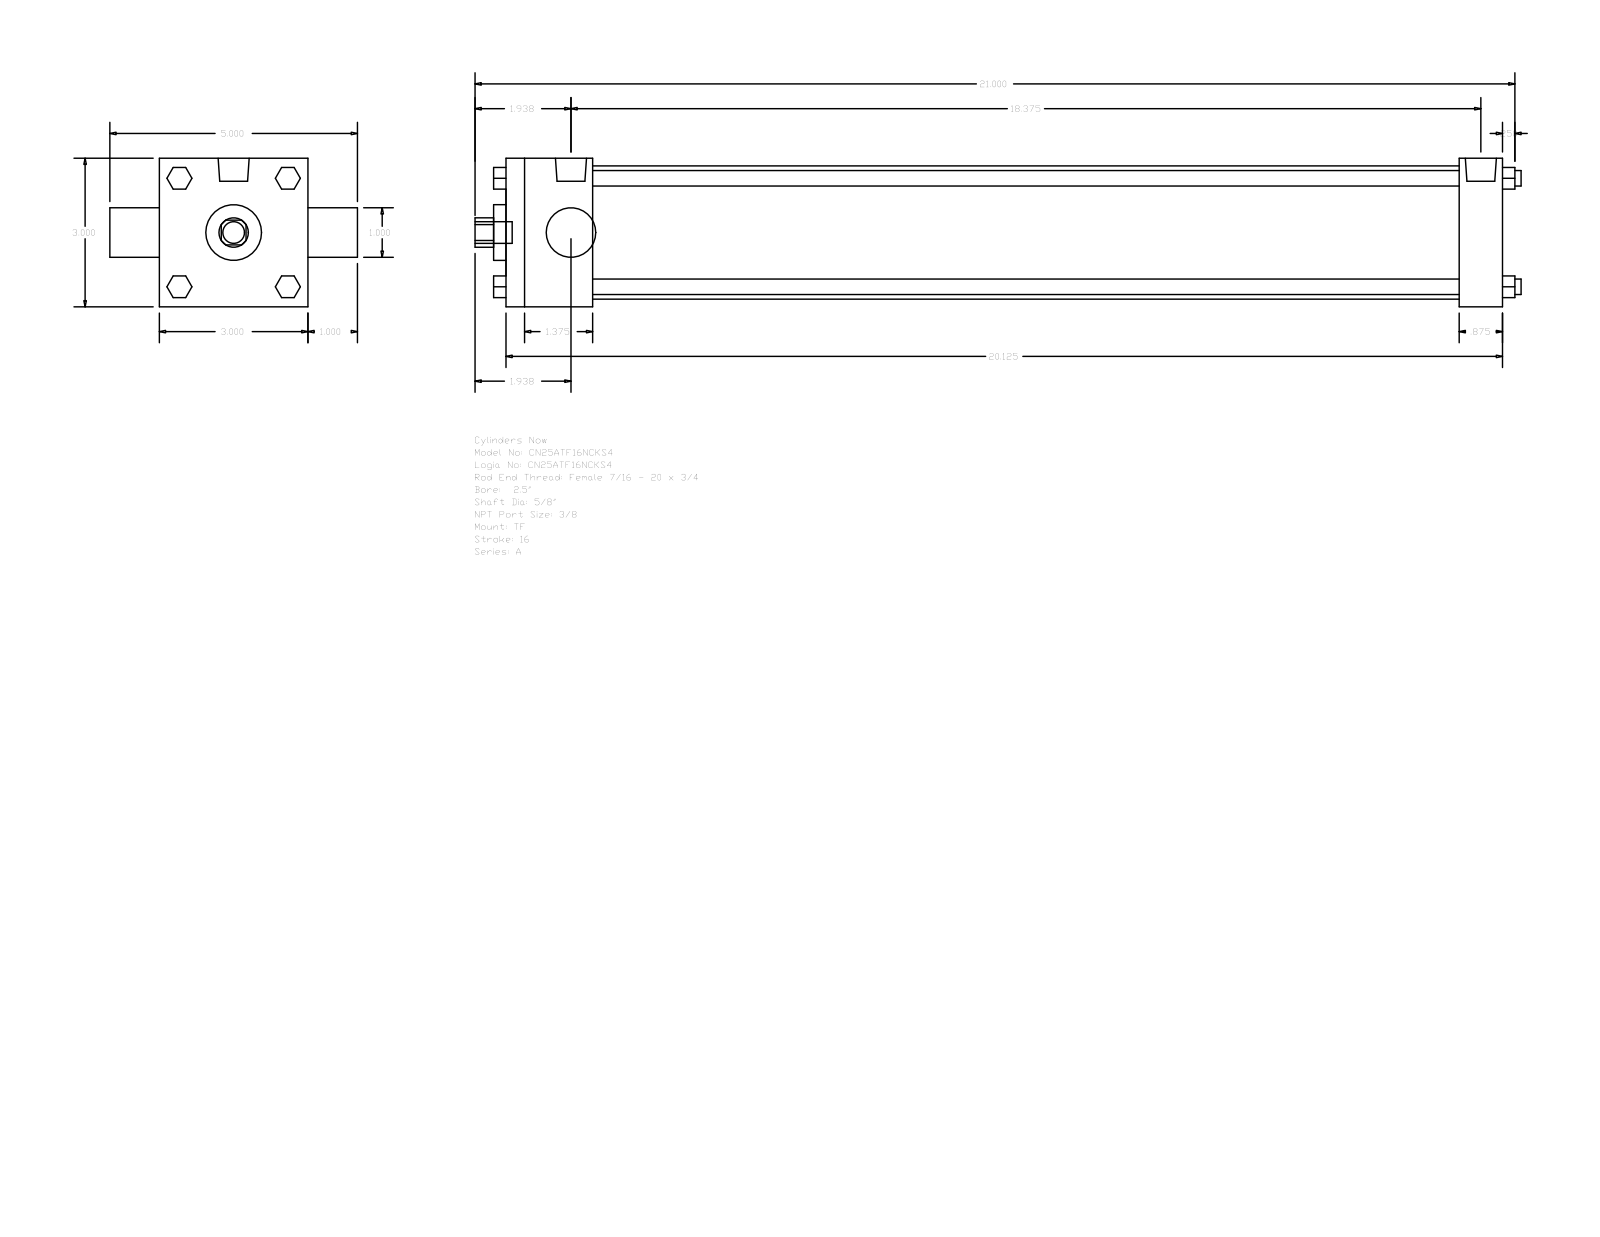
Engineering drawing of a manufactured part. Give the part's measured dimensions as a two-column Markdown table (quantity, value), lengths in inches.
| quantity | value |
| --- | --- |
| part name | A_TF__0250_0.625 |
| STEP written by | GSSL Pune (CONFIG_CONTROL_DESIGN) |
| units | inches |
| bodies | 0 solids, 120 faces (92 planar, 28 cylindrical, 0 other) |
| overall size | 21.125 × 5 × 3 |
| round holes (diameter × count) | 0.625 × 1, 1 × 1, 1.125 × 1, 2.69 × 1 |
| round bosses / shafts (diameter × count) | 0.313 × 4, 0.219 × 3, 0.627 × 2, 0.437 × 1 |
| partial cylindrical surfaces (radius × count) | 0.297 × 1 |
| main face-to-face distances | 3, 20.125, 1.75, 19.25, 17.5, 18.375, 0.875, 1, 4, 0.25 |
